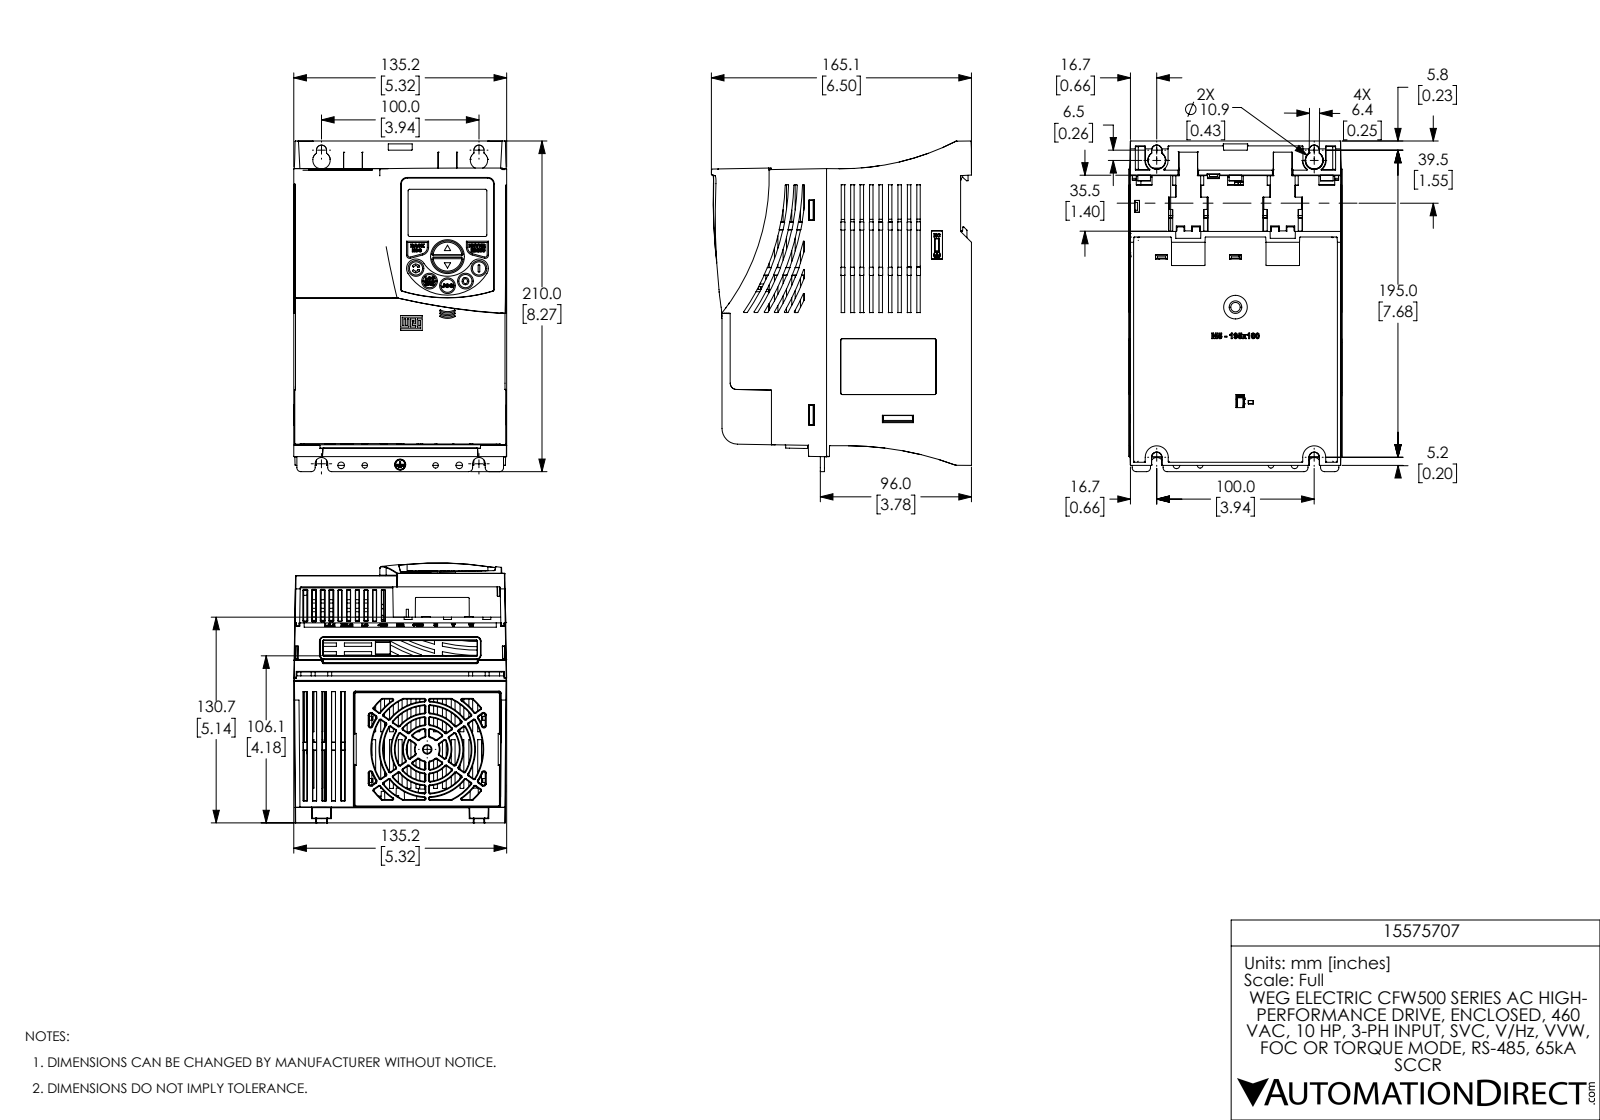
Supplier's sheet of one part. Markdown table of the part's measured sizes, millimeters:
| quantity | value |
| --- | --- |
| part name | CFW50X_FRAME_C_IP20_PAR fXT r1 coord r1 |
| STEP written by | SolidWorks 2017 (AUTOMOTIVE_DESIGN) |
| units | millimeters |
| bodies | 10 solids, 5734 faces (2633 planar, 1093 cylindrical, 2008 other) |
| overall size | 210 × 165.1 × 135.2 |
| volume | 458 300 mm³ |
| surface area | 386 500 mm² |
| round holes (diameter × count) | 10 × 3, 2.5 × 2, 3.5 × 2, 4.2 × 2, 9.8 × 2, 3.9 × 1, 20 × 1, 21.5 × 1 |
| round bosses / shafts (diameter × count) | 10 × 2, 4.4 × 1 |
| partial cylindrical surfaces (radius × count) | 0.3 × 399, 0.2 × 154, 0.5 × 42, 1 × 31, 2.5 × 10, 4 × 4, 9.7 × 3, 10.5 × 3 |
| main face-to-face distances | 3.1, 2, 3.1, 148.4, 1.4, 147, 1.5, 117, 30, 31.4 |
| hole center spacings | 11.8, 22.8, 15, 19.3, 21.4, 23.1, 32.4, 36.9 |
